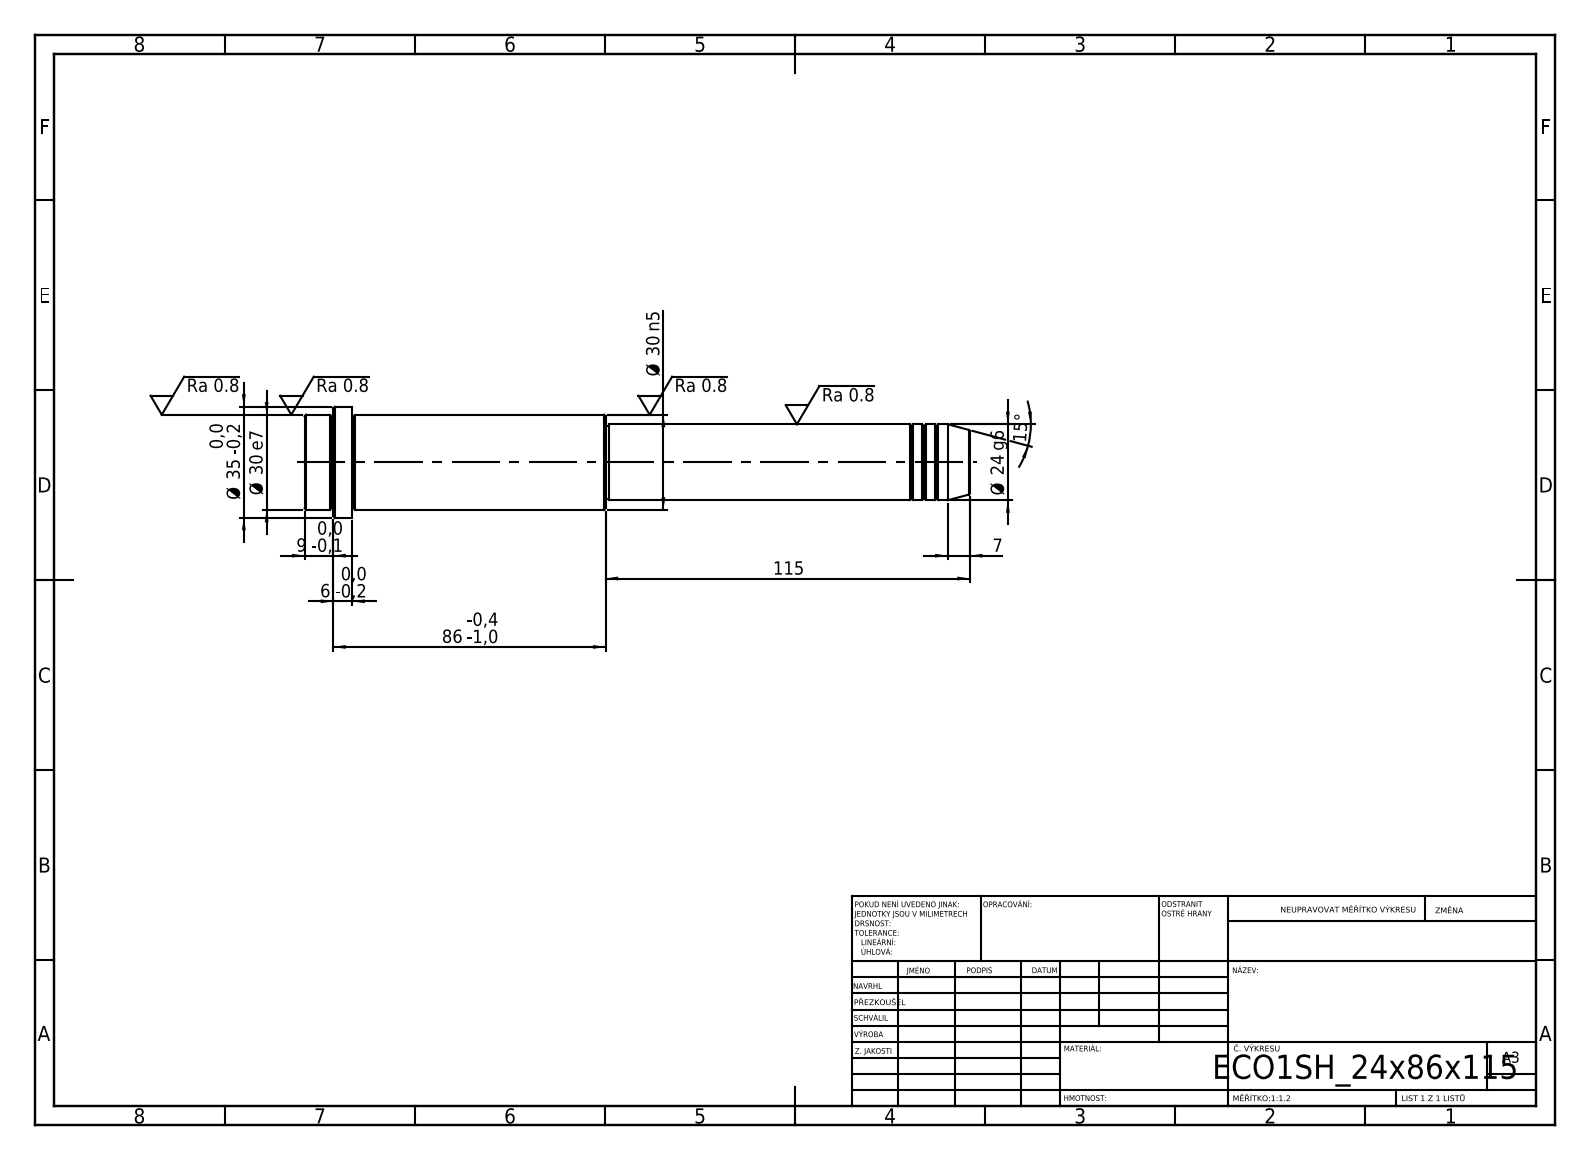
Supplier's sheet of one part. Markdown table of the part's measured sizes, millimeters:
| quantity | value |
| --- | --- |
| STEP written by | SolidWorks 2019 (CONFIG_CONTROL_DESIGN) |
| units | millimeters |
| bodies | 1 solid, 52 faces (6 planar, 16 cylindrical, 30 other) |
| overall size | 210 × 35 × 35 |
| volume | 120 003 mm³ |
| surface area | 19 684 mm² |
| round bosses / shafts (diameter × count) | 35 × 1, 30 × 1, 24 × 1, 23 × 1 |
| main face-to-face distances | 210, 195, 15, 115, 80, 95, 201, 86, 6, 9 |
